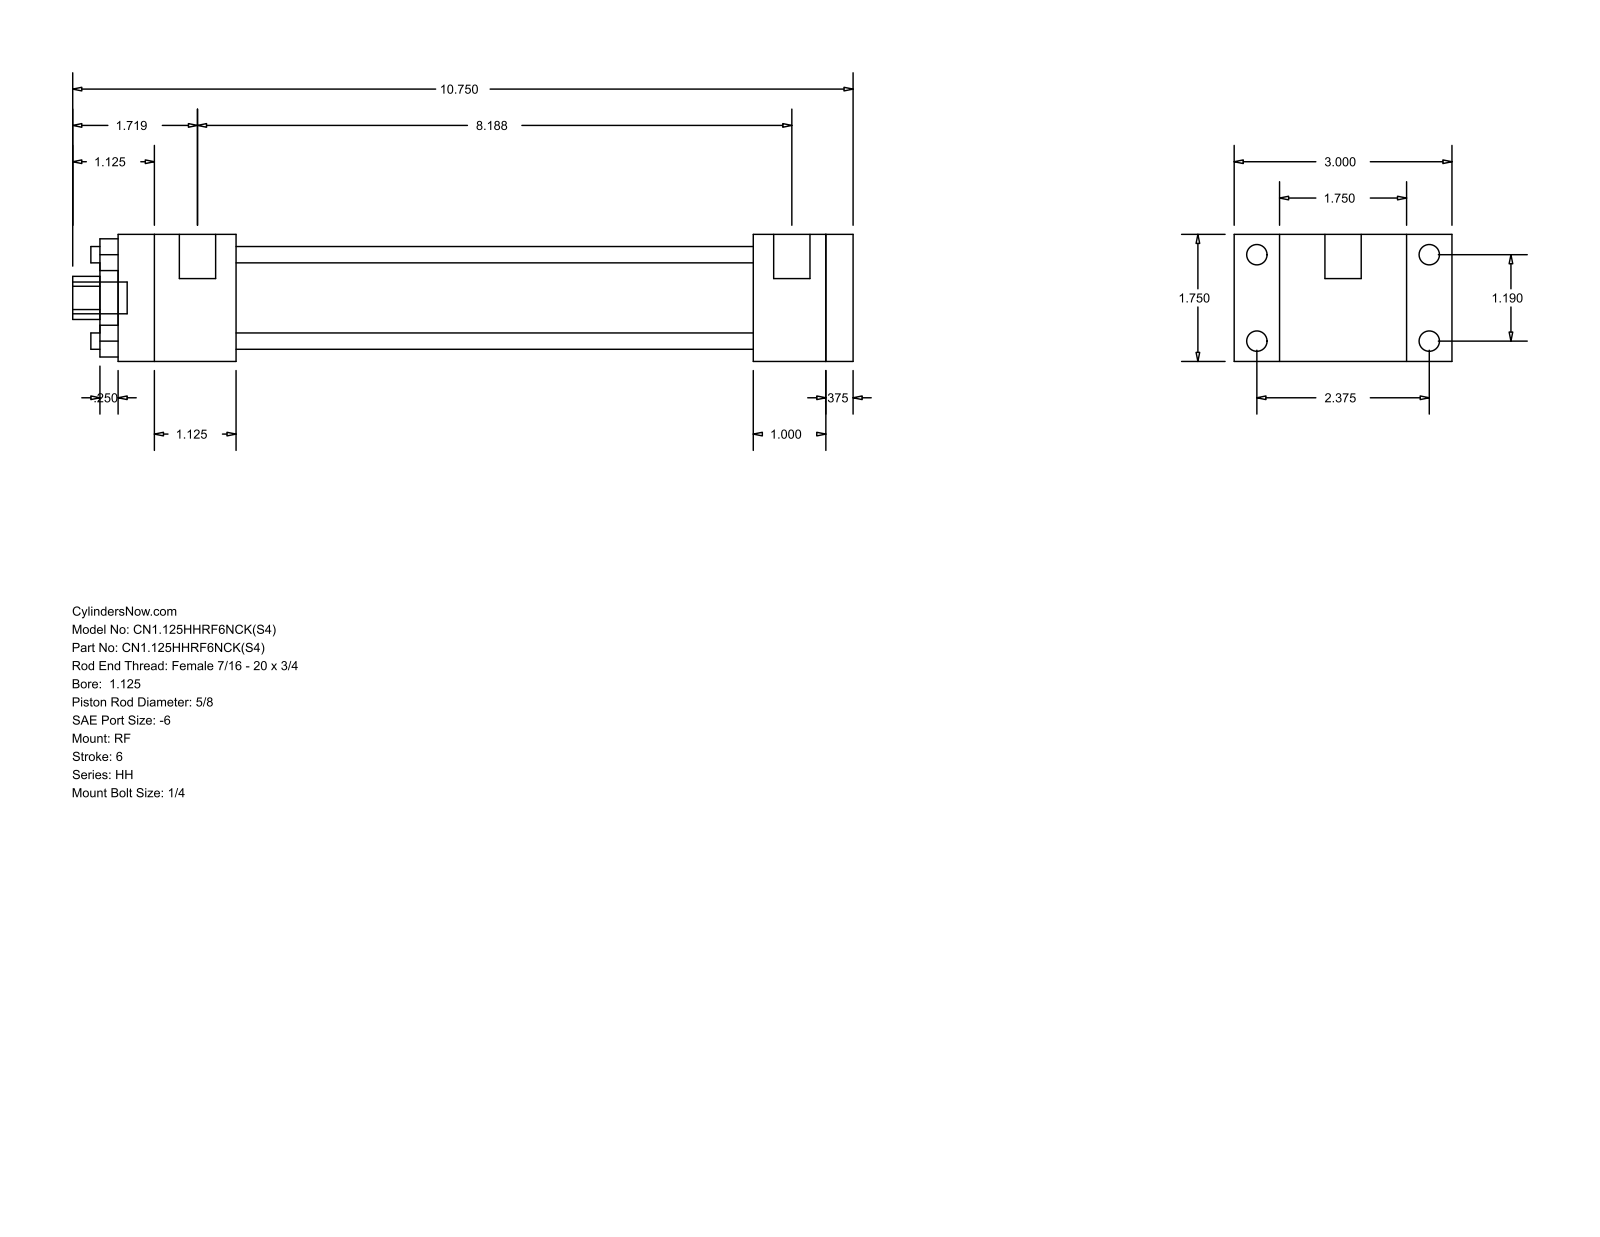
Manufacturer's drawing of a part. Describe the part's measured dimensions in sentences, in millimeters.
The part is named "HH_RF__0112_0.625". Its 3-D file was written by "GSSL Pune (CONFIG_CONTROL_DESIGN)". It is 0 solids with 92 faces: 64 planar, 28 cylindrical and 0 other. Overall it measures 273.05 by 76.2 by 44.45 millimeters. Round holes: 4 of diameter 5.71, 1 of diameter 15.88, 1 of diameter 28.57, 1 of diameter 34.92. Round bosses or shafts: 4 of diameter 7.14, 4 of diameter 5.56, 2 of diameter 12.7, 1 of diameter 11.11. Partial cylindrical surfaces (rounded edges, fillets, slot ends): 1 of radius 7.54. The main face-to-face distances are 44.46, 9.53, 257.17, 15.87, 206.37, 215.9, 180.97, 25.4, 34.93, 41.27. The hole center spacings are 21.37, 30.22, 42.74.
